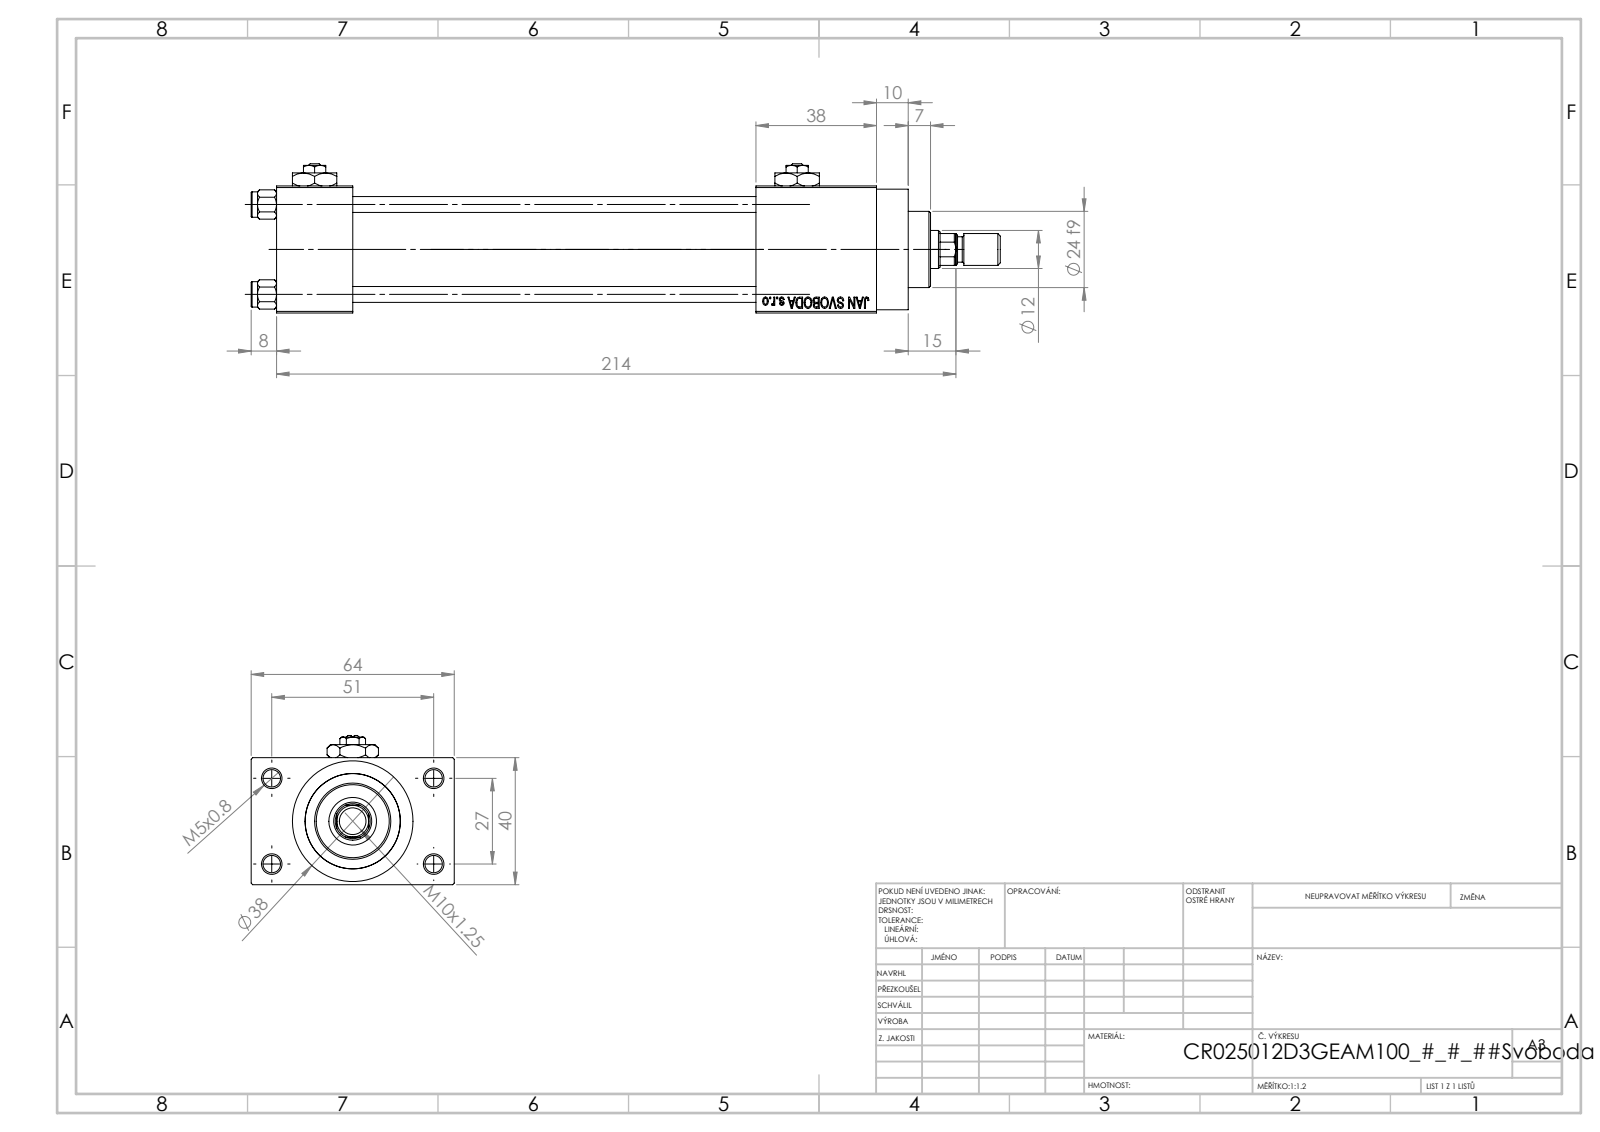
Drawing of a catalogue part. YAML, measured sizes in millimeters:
part_name: "NUT_M5_D; V215_VC_A; V215CR_D_TYCINKA; V215CR_VCP_D (+3 more)"
step_written_by: "SolidWorks 2019 (CONFIG_CONTROL_DESIGN)"
units: millimeters
bodies: {solids: 14, faces: 1216, planar: 546, cylindrical: 104, other: 566}
overall_size: [236, 64, 47]
volume: 211687
surface_area: 86042
round_holes:
  - {diameter: 5, count: 4}
  - {diameter: 5.5, count: 4}
  - {diameter: 20, count: 3}
  - {diameter: 7, count: 2}
  - {diameter: 13.16, count: 2}
  - {diameter: 6.5, count: 1}
  - {diameter: 12, count: 1}
  - {diameter: 15, count: 1}
  - {diameter: 25, count: 1}
  - {diameter: 30, count: 1}
round_bosses_or_shafts:
  - {diameter: 8, count: 5}
  - {diameter: 38, count: 1}
  - {diameter: 31, count: 1}
  - {diameter: 24, count: 1}
  - {diameter: 10, count: 1}
partial_cylinders:
  - {radius: 5.5, count: 1}
face_to_face_distances: [40, 12, 52, 127, 24, 151, 64, 38, 165, 189]
hole_center_spacings: [11.37, 20.01, 28.3, 28.85, 29.89, 39.66, 48.34, 27]
